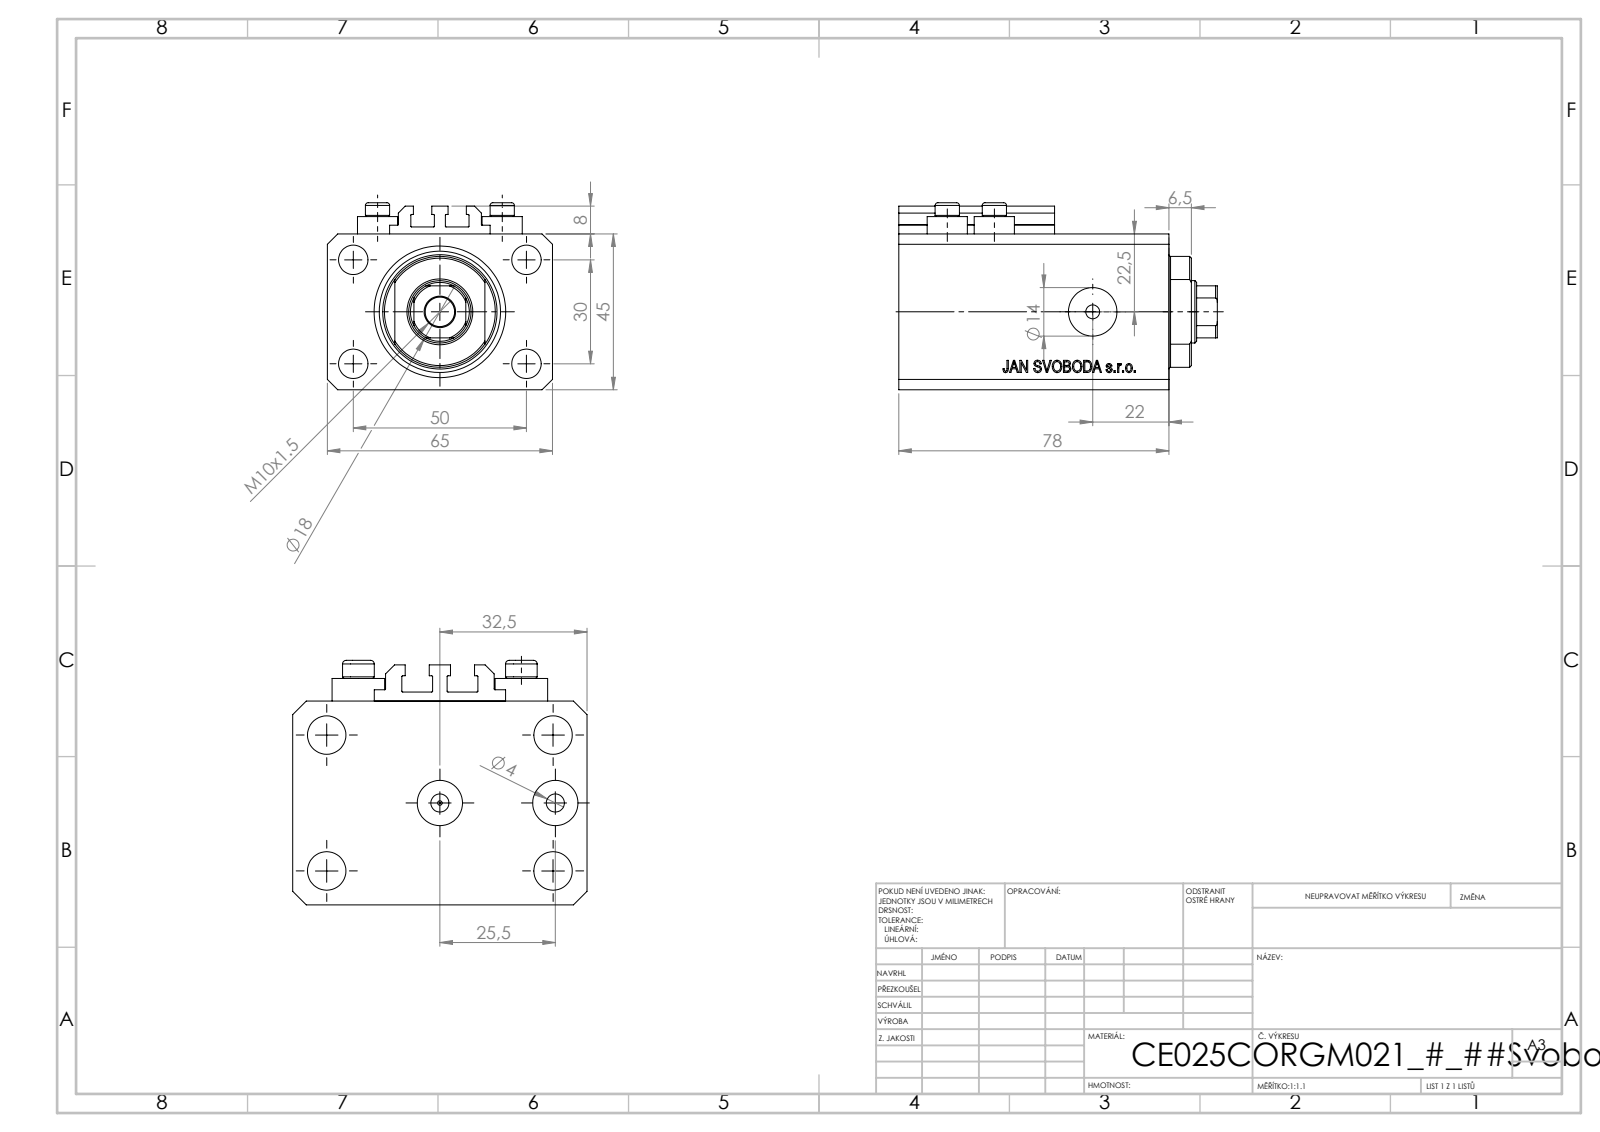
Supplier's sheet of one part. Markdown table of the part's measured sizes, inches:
| quantity | value |
| --- | --- |
| part name | V250CE_C_Body; ALLEN BOLT V250CE; V250CE_C_VCP; V250CE_VC_C |
| STEP written by | SolidWorks 2019 (CONFIG_CONTROL_DESIGN) |
| units | inches |
| bodies | 8 solids, 1042 faces (504 planar, 92 cylindrical, 446 other) |
| overall size | 3.622 × 2.559 × 2.126 |
| volume | 13.06 in³ |
| surface area | 90.27 in² |
| round holes (diameter × count) | 0.157 × 8, 0.335 × 5, 0.394 × 2, 0.551 × 2, 0.049 × 1, 0.709 × 1, 0.984 × 1, 1.496 × 1 |
| round bosses / shafts (diameter × count) | 0.457 × 4, 0.276 × 4 |
| partial cylindrical surfaces (radius × count) | 0.008 × 10, 0.335 × 1, 0.63 × 1 |
| main face-to-face distances | 1.772, 2.559, 0.551, 3.071, 2.52, 0.272, 2.248, 2.799, 0.118, 1.85 |
| hole center spacings | 1.148, 0.535, 0.591, 1.181, 1.417, 1.515, 1.969, 2.074 |
